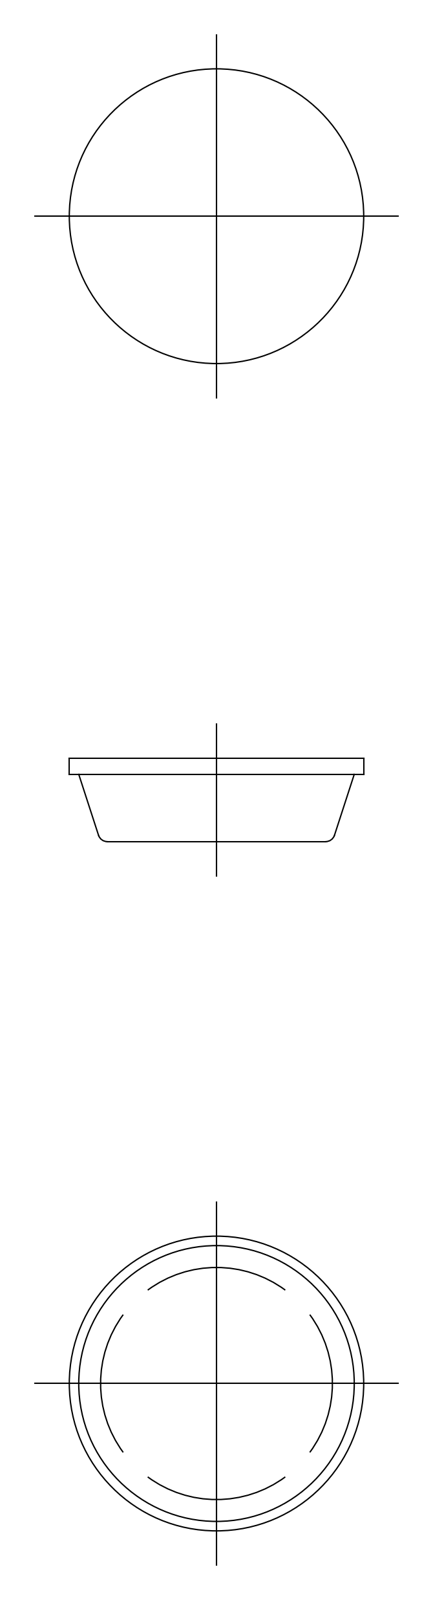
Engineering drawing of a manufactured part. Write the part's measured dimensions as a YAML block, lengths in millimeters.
part_name: "rubber foot"
step_written_by: "CADfix (AUTOMOTIVE_DESIGN)"
units: millimeters
bodies: {solids: 1, faces: 9, planar: 0, cylindrical: 0, other: 9}
overall_size: [12.7, 12.7, 3.6]
volume: 362
surface_area: 351
